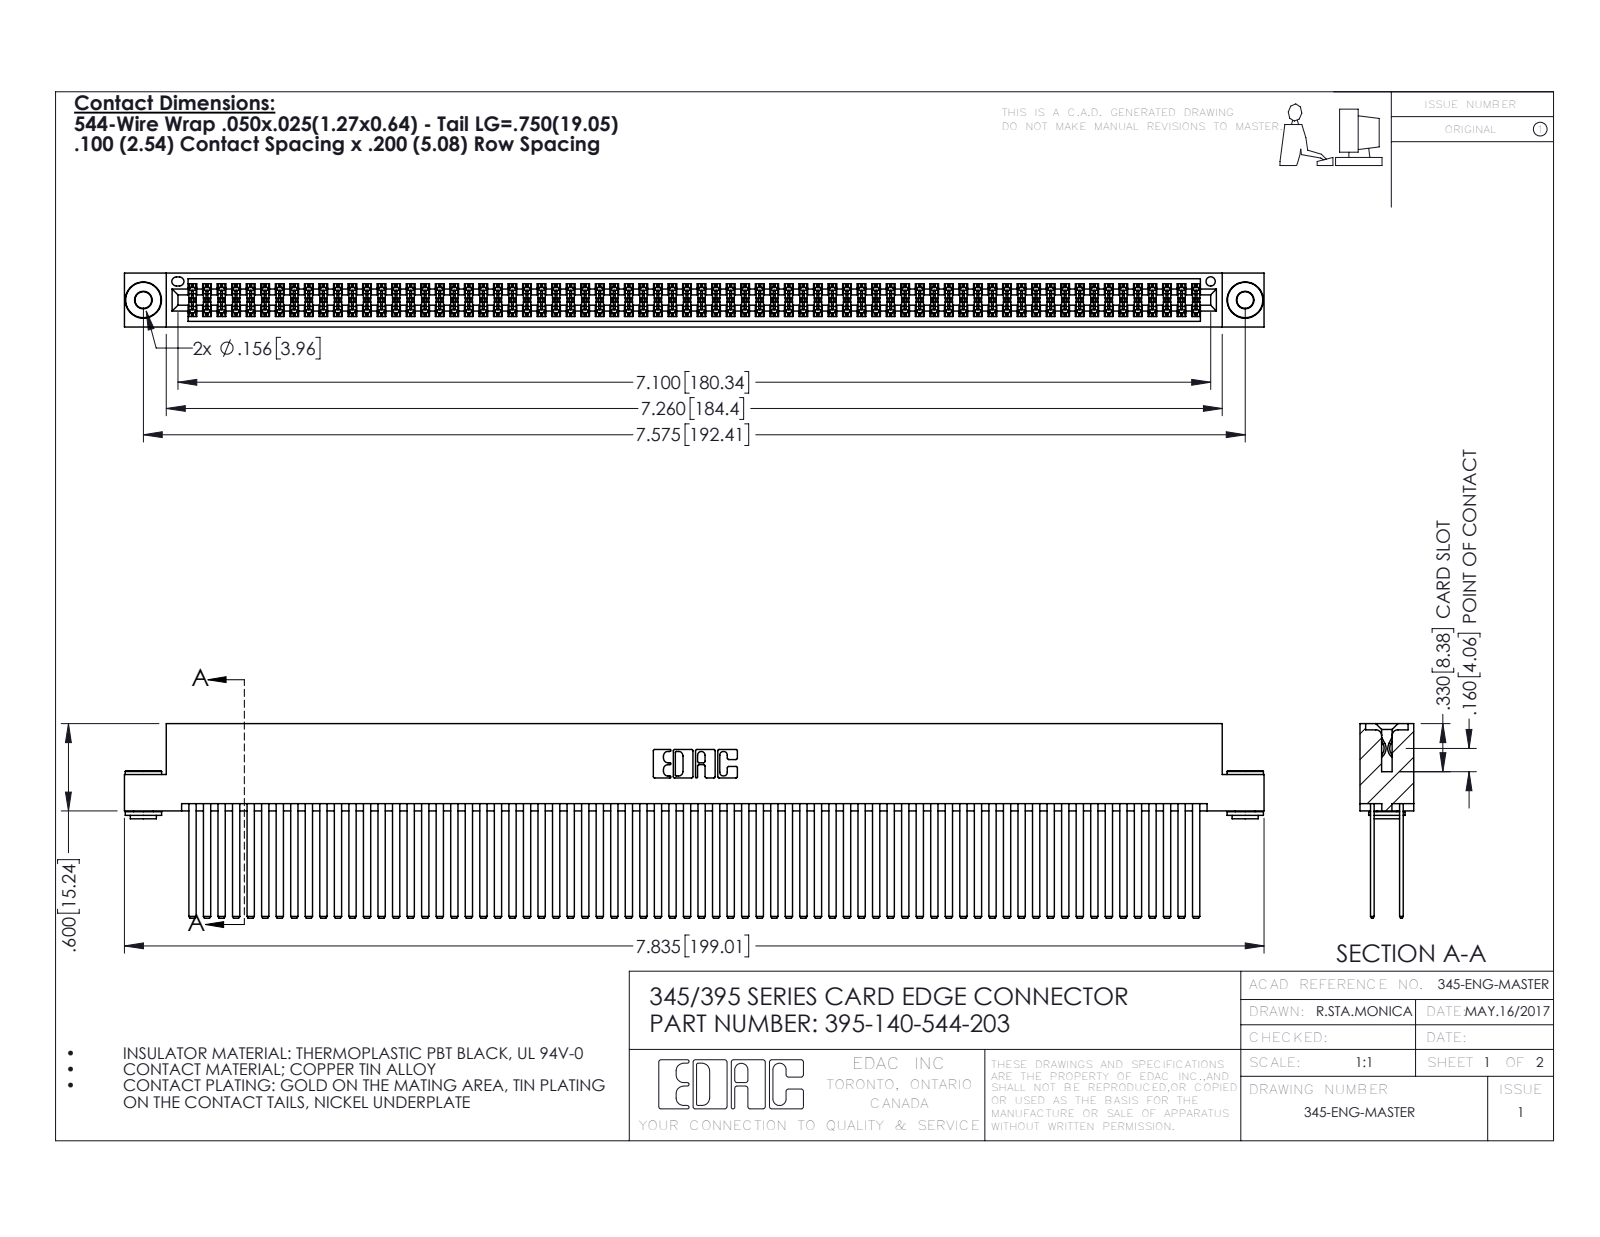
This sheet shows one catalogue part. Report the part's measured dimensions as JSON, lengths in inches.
{"part_name": "395-140-544-203; 345-292-001_345-293-144; 345-250-002_345-250-002-102; 345 Part_Flush Mounting Lugs - 0.156 Dia-TH", "step_written_by": "SolidWorks 2016 (CONFIG_CONTROL_DESIGN)", "units": "inches", "bodies": {"solids": 143, "faces": 6324, "planar": 4150, "cylindrical": 2166, "other": 8}, "overall_size": [7.835, 1.337, 0.37], "volume_in3": 1.317, "surface_area_in2": 59.5, "round_holes": [[0.116, 2], [0.156, 2], [0.064, 1]], "round_bosses_or_shafts": [[0.25, 2], [0.18, 2], [0.136, 2]], "partial_cylinders_radius": [[0.006, 210], [0.01, 22], [0.007, 6], [0.031, 6], [0.026, 3], [0.014, 2], [0.019, 2], [0.022, 2]], "face_to_face_distances": [0.2, 0.025, 0.072, 0.098, 0.272, 0.298, 0.225, 0.175, 0.37, 0.05], "hole_center_spacings": [0.27, 7.339, 7.575]}
